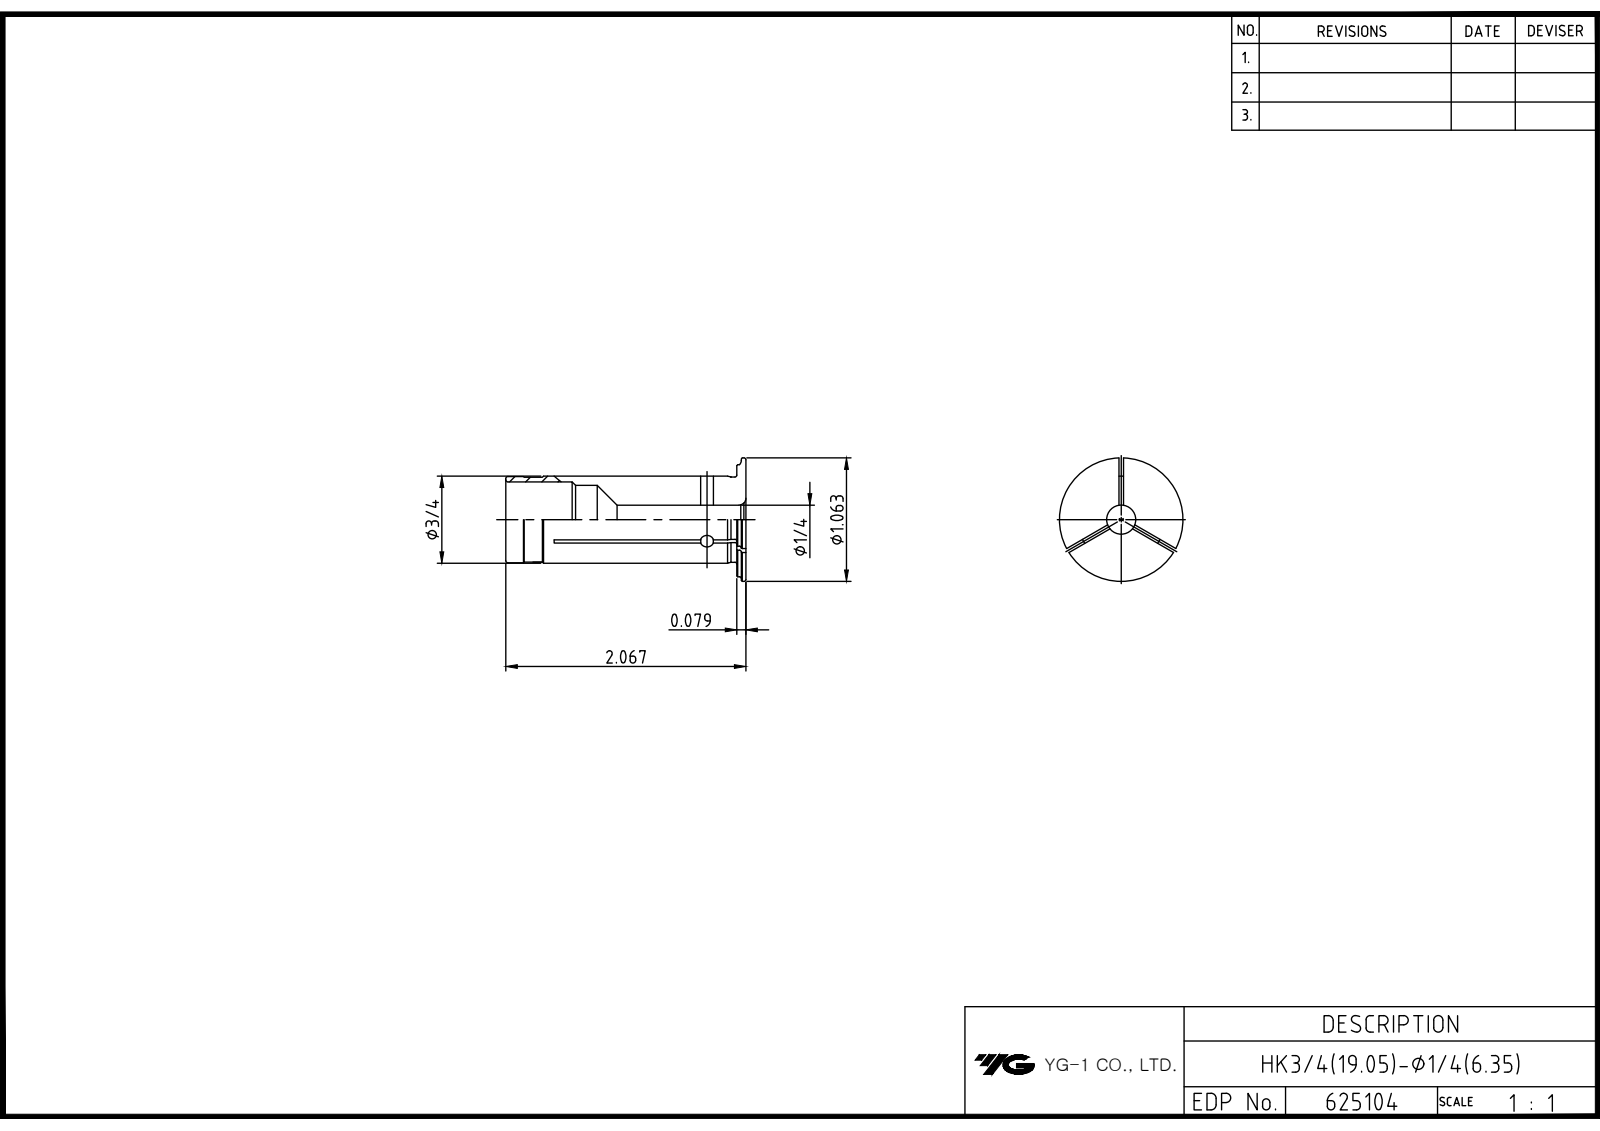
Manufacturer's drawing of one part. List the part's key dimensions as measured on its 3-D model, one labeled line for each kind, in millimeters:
Part name (STEP PRODUCT): HK19_05-6_35
STEP written by: PRO/ENGINEER BY PARAMETRIC TECHNOLOGY CORPORATION, 2012130 (CONFIG_CONTROL_DESIGN)
Units: millimetres
Bodies: 1 solid, 92 faces (22 planar, 32 cylindrical, 38 other)
Overall size (bounding box): 52.5 × 27 × 26.99
Volume: 9 190 mm³ · Surface area: 6 814 mm²
Round holes (diameter × count): ⌀6.35 ×1, ⌀15 ×1, ⌀16.5 ×1
Round bosses / shafts (diameter × count): ⌀27 ×1, ⌀24.05 ×1, ⌀19.05 ×1, ⌀18.85 ×1, ⌀18.65 ×1, ⌀18.55 ×1
Partial cylindrical surfaces — rounded edges, fillets, slot ends (radius × count): R1.45 ×3, R37.5 ×3
Main face-to-face distances: 1, 2, 50.5, 51.5, 52.5
